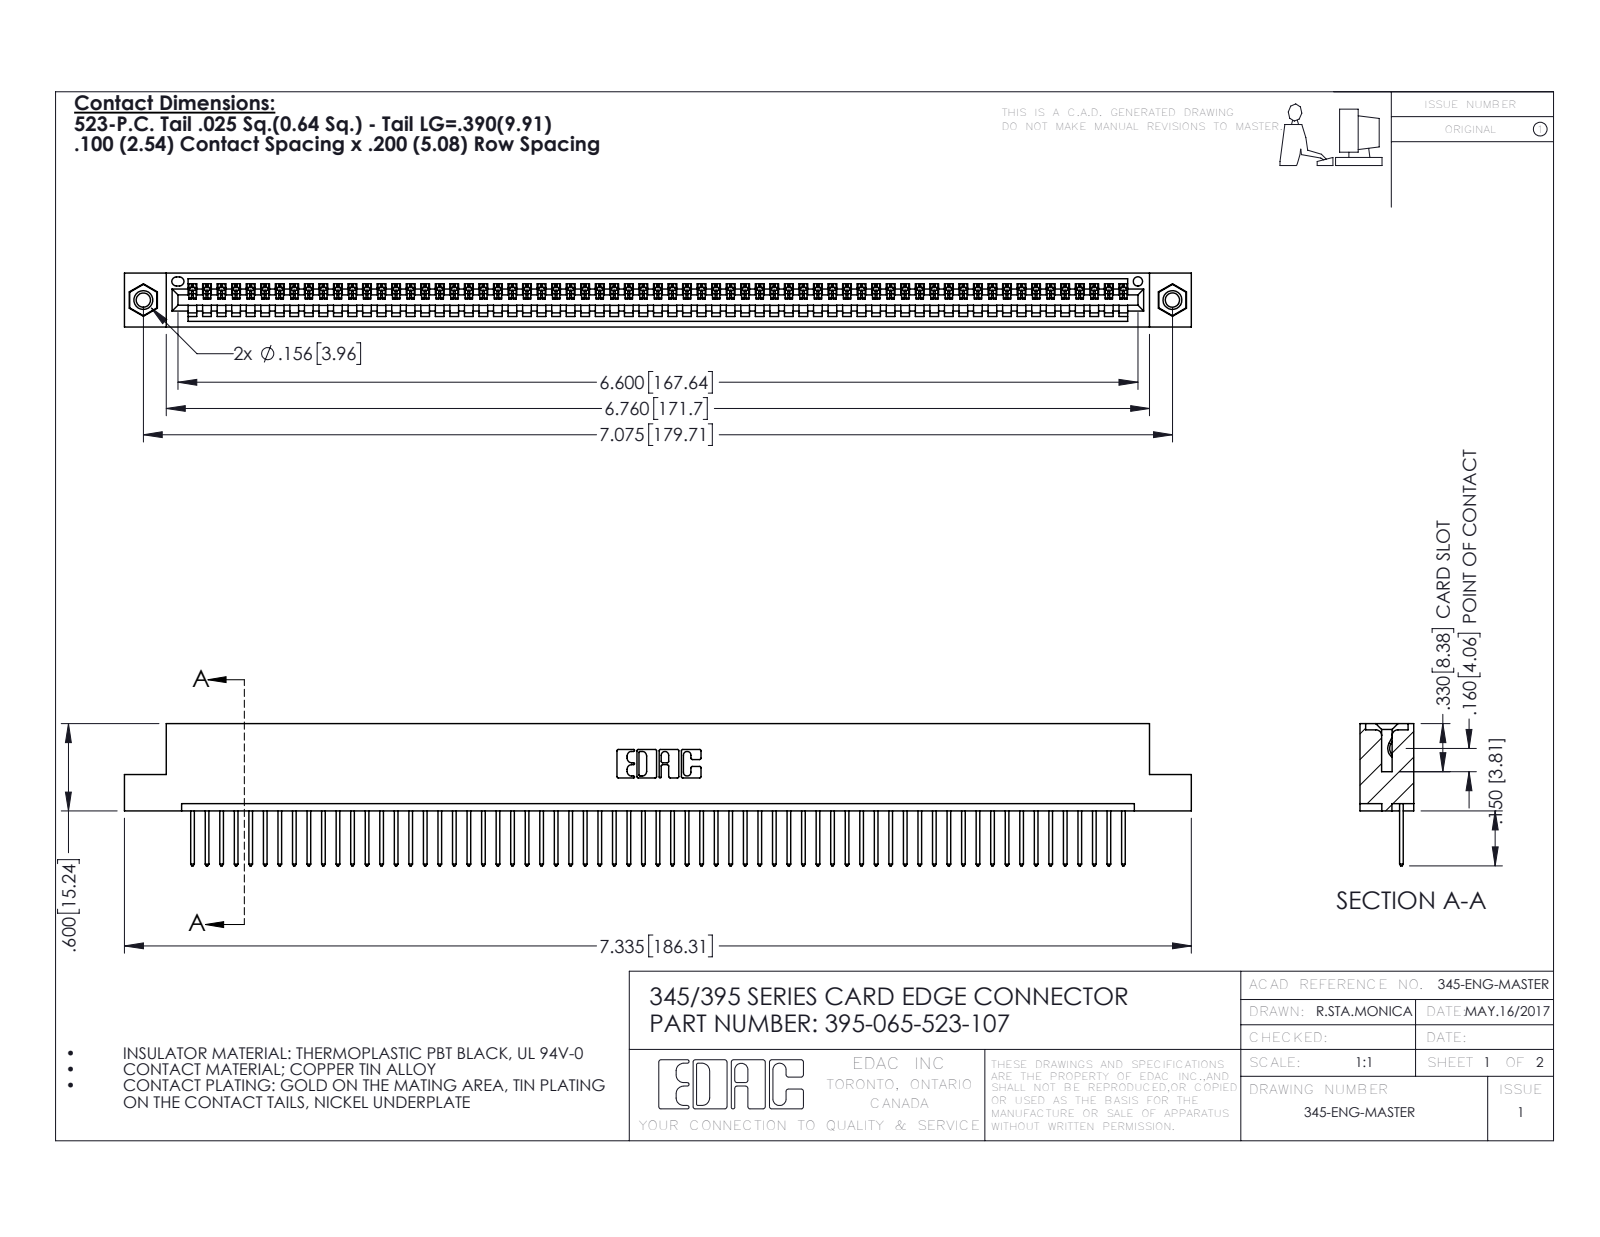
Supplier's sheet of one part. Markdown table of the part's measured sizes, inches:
| quantity | value |
| --- | --- |
| part name | 395-065-523-107; 345-250-001_345-250-005-103; 345-292-001_345-293-123; 345 Part_Flush Mounting Lugs - 0.156 Dia-TI |
| STEP written by | SolidWorks 2016 (CONFIG_CONTROL_DESIGN) |
| units | inches |
| bodies | 68 solids, 3956 faces (2712 planar, 1228 cylindrical, 16 other) |
| overall size | 7.335 × 0.977 × 0.37 |
| volume | 1.089 in³ |
| surface area | 37.4 in² |
| round holes (diameter × count) | 0.098 × 2, 0.125 × 2, 0.156 × 2, 0.064 × 1 |
| round bosses / shafts (diameter × count) | 0.155 × 2 |
| partial cylindrical surfaces (radius × count) | 0.006 × 130, 0.01 × 130, 0.01 × 22, 0.007 × 6, 0.031 × 6, 0.026 × 3, 0.031 × 2, 0.04 × 2 |
| main face-to-face distances | 0.072, 0.298, 0.37, 0.2, 0.098, 0.272, 0.025, 0.225, 0.149, 0.072 |
| hole center spacings | 0.27, 6.839, 7.075 |
